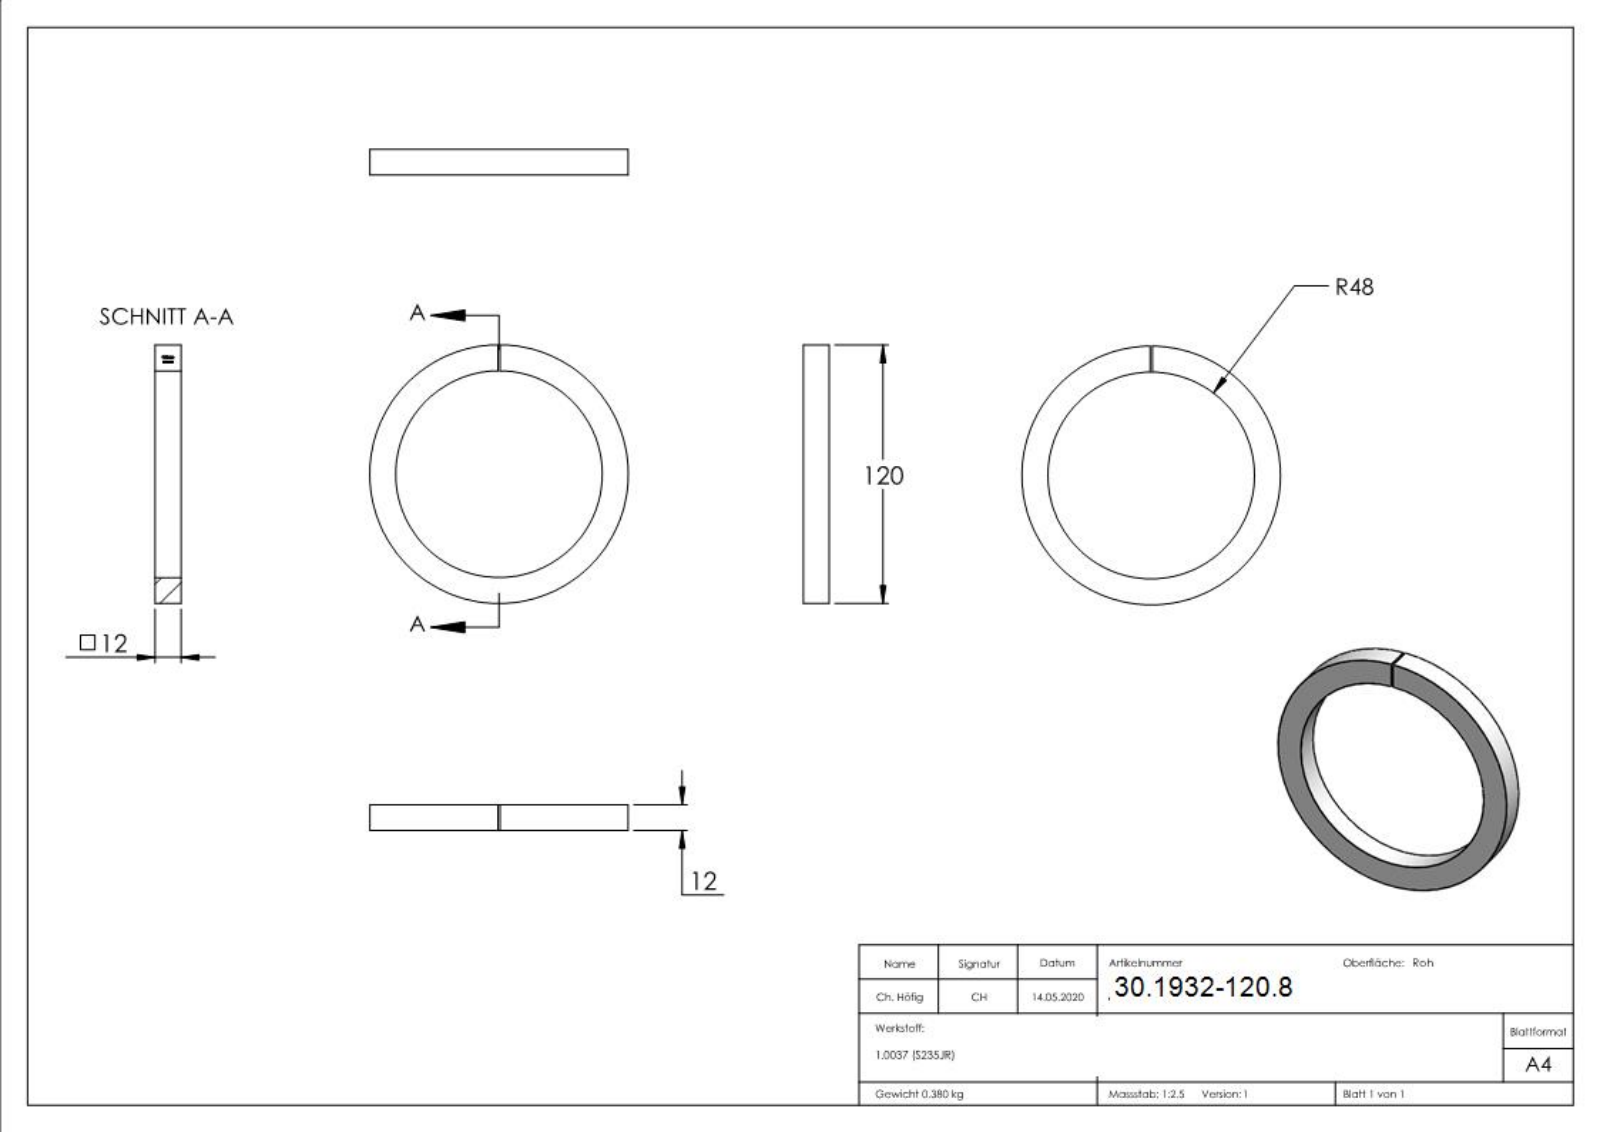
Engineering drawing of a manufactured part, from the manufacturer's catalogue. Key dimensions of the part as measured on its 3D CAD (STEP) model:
Part name (STEP PRODUCT): 5635-120
STEP written by: SolidWorks 2015 (CONFIG_CONTROL_DESIGN)
Units: millimetres
Bodies: 1 solid, 217 faces (113 planar, 2 cylindrical, 102 other)
Overall size (bounding box): 120 × 120 × 12
Volume: 48 714 mm³ · Surface area: 16 531 mm²
Round holes (diameter × count): ⌀96 ×1
Round bosses / shafts (diameter × count): ⌀120 ×1
Main face-to-face distances: 12, 1, 1.1, 1.78, 2.12, 0.83, 0.99, 2.77, 1.21, 3.33
